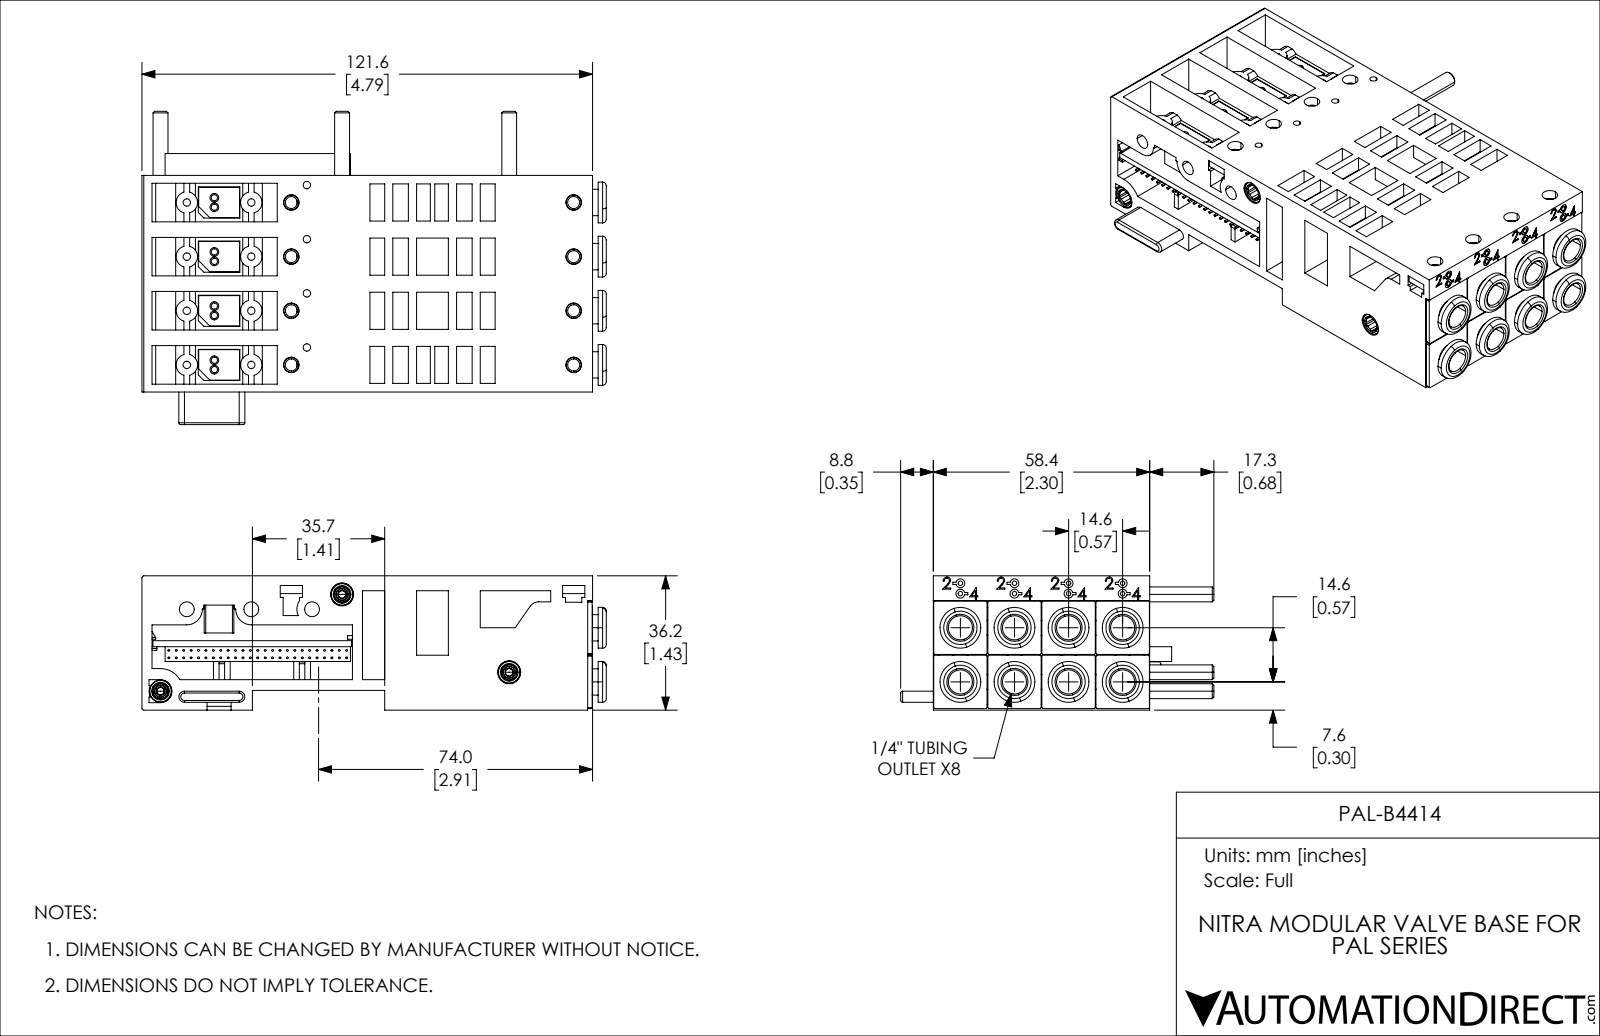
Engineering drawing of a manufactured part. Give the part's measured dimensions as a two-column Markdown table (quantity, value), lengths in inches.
| quantity | value |
| --- | --- |
| part name | PAL-B4414 |
| STEP written by | SolidWorks 2019 (CONFIG_CONTROL_DESIGN) |
| units | inches |
| bodies | 7 solids, 1682 faces (918 planar, 586 cylindrical, 178 other) |
| overall size | 4.933 × 3.327 × 1.425 |
| volume | 9.474 in³ |
| surface area | 128.4 in² |
| round holes (diameter × count) | 0.02 × 50, 0.079 × 12, 0.128 × 11, 0.094 × 8, 0.165 × 8, 0.256 × 8, 0.157 × 3, 0.244 × 2, 0.189 × 1 |
| round bosses / shafts (diameter × count) | 0.433 × 8, 0.28 × 8, 0.228 × 8, 0.047 × 8, 0.236 × 3, 0.157 × 3, 0.177 × 2 |
| partial cylindrical surfaces (radius × count) | 0.02 × 11, 0.098 × 8, 0.295 × 8, 0.394 × 8, 0.157 × 6, 0.037 × 5, 0.039 × 5, 0.026 × 4 |
| main face-to-face distances | 1.425, 0.063, 0.323, 0.752, 0.673, 0.736, 0.575, 0.413, 0.339, 0.689 |
| hole center spacings | 0.575, 0.079, 0.157, 0.236, 0.315, 0.472, 1.15, 0.394 |
